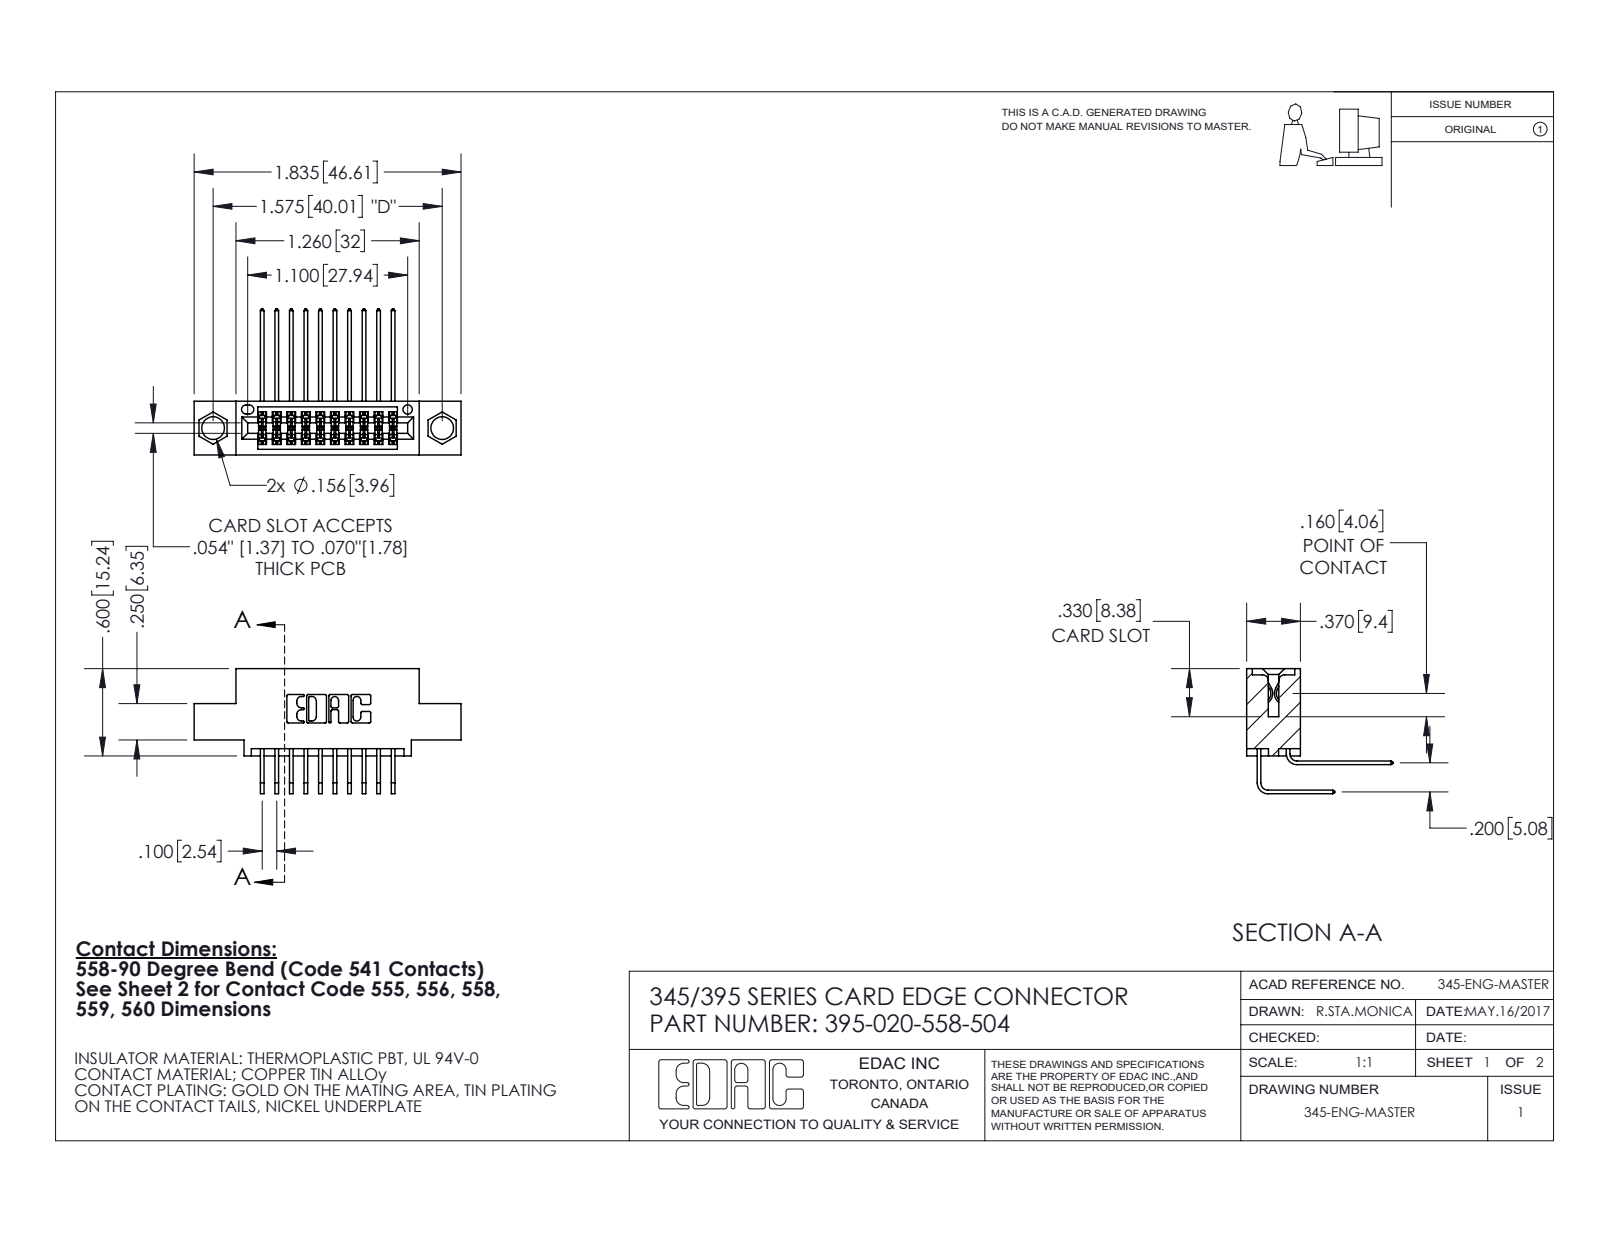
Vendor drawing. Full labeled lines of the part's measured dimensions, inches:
Part name (STEP PRODUCT): 345 Part_0.110 Offset - 0.156 Dia-TI; 345-292-001_558 Tail - 2; 395-020-558-504; 345-292-001_558 559 Tail - 1
STEP written by: SolidWorks 2020 (CONFIG_CONTROL_DESIGN)
Units: inches
Bodies: 21 solids, 1184 faces (798 planar, 386 cylindrical, 0 other)
Overall size (bounding box): 1.835 × 1.005 × 0.859
Volume: 0.254 in³ · Surface area: 9.341 in²
Round holes (diameter × count): ⌀0.156 ×2, ⌀0.064 ×1
Partial cylindrical surfaces — rounded edges, fillets, slot ends (radius × count): R0.006 ×30, R0.01 ×22, R0.007 ×6, R0.031 ×6, R0.026 ×3, R0.014 ×2, R0.019 ×2, R0.022 ×2
Main face-to-face distances: 0.2, 0.072, 0.298, 0.37, 0.098, 0.272, 0.025, 0.1, 0.6, 0.225
Hole centre spacings: 0.27, 1.344, 1.575
